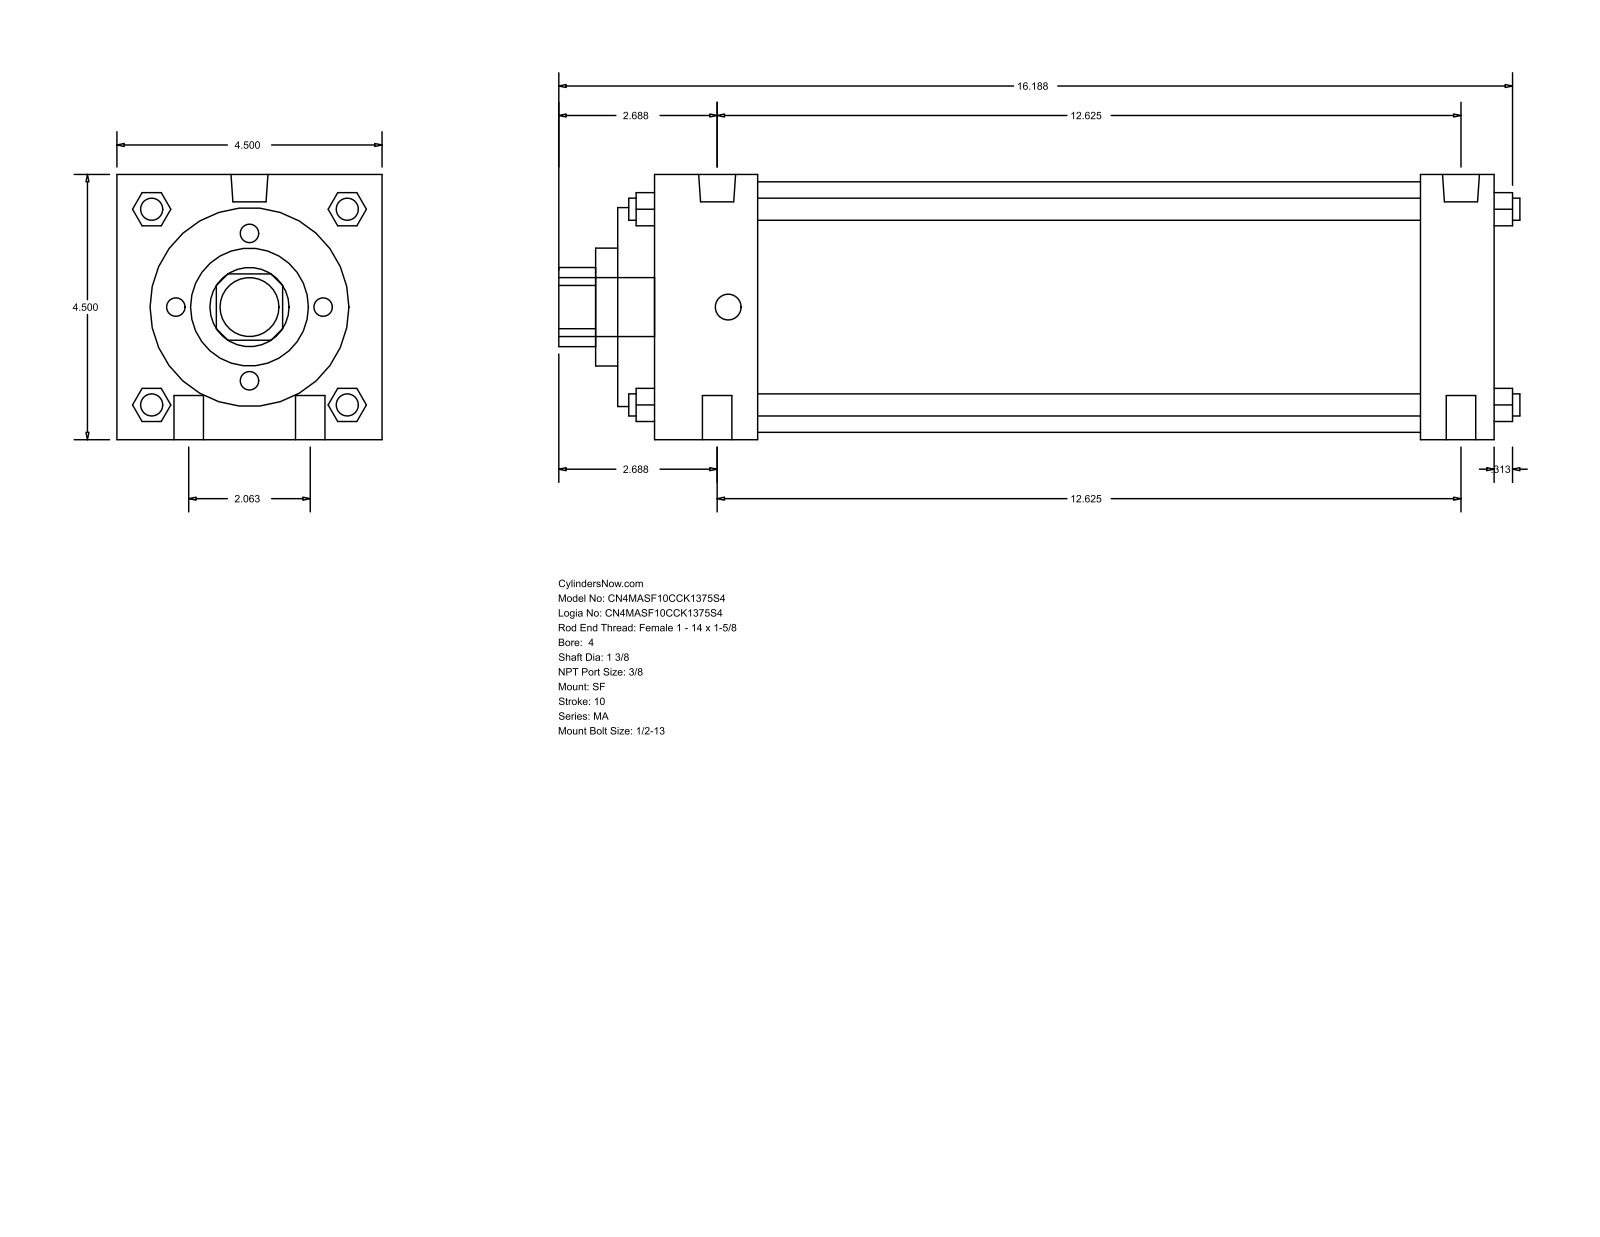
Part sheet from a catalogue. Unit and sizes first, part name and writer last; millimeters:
Units: millimetres
Overall size (bounding box): 414.34 × 114.3 × 114.3
Round holes (diameter × count): ⌀34.92 ×1, ⌀50.8 ×1, ⌀85.72 ×1, ⌀107.95 ×1
Round bosses / shafts (diameter × count): ⌀12.7 ×4, ⌀9.53 ×4, ⌀15.93 ×2, ⌀11.11 ×2, ⌀25.4 ×1
Partial cylindrical surfaces — rounded edges, fillets, slot ends (radius × count): R17.06 ×1
Main face-to-face distances: 114.3, 361.96, 15.87, 377.83, 346.08, 330.21, 31.75, 60.32, 44.45, 285.76
Bodies: 0 solids, 126 faces (95 planar, 31 cylindrical, 0 other)
Part name (STEP PRODUCT): MA_SF__0400_1.375
STEP written by: GSSL Pune (CONFIG_CONTROL_DESIGN)
